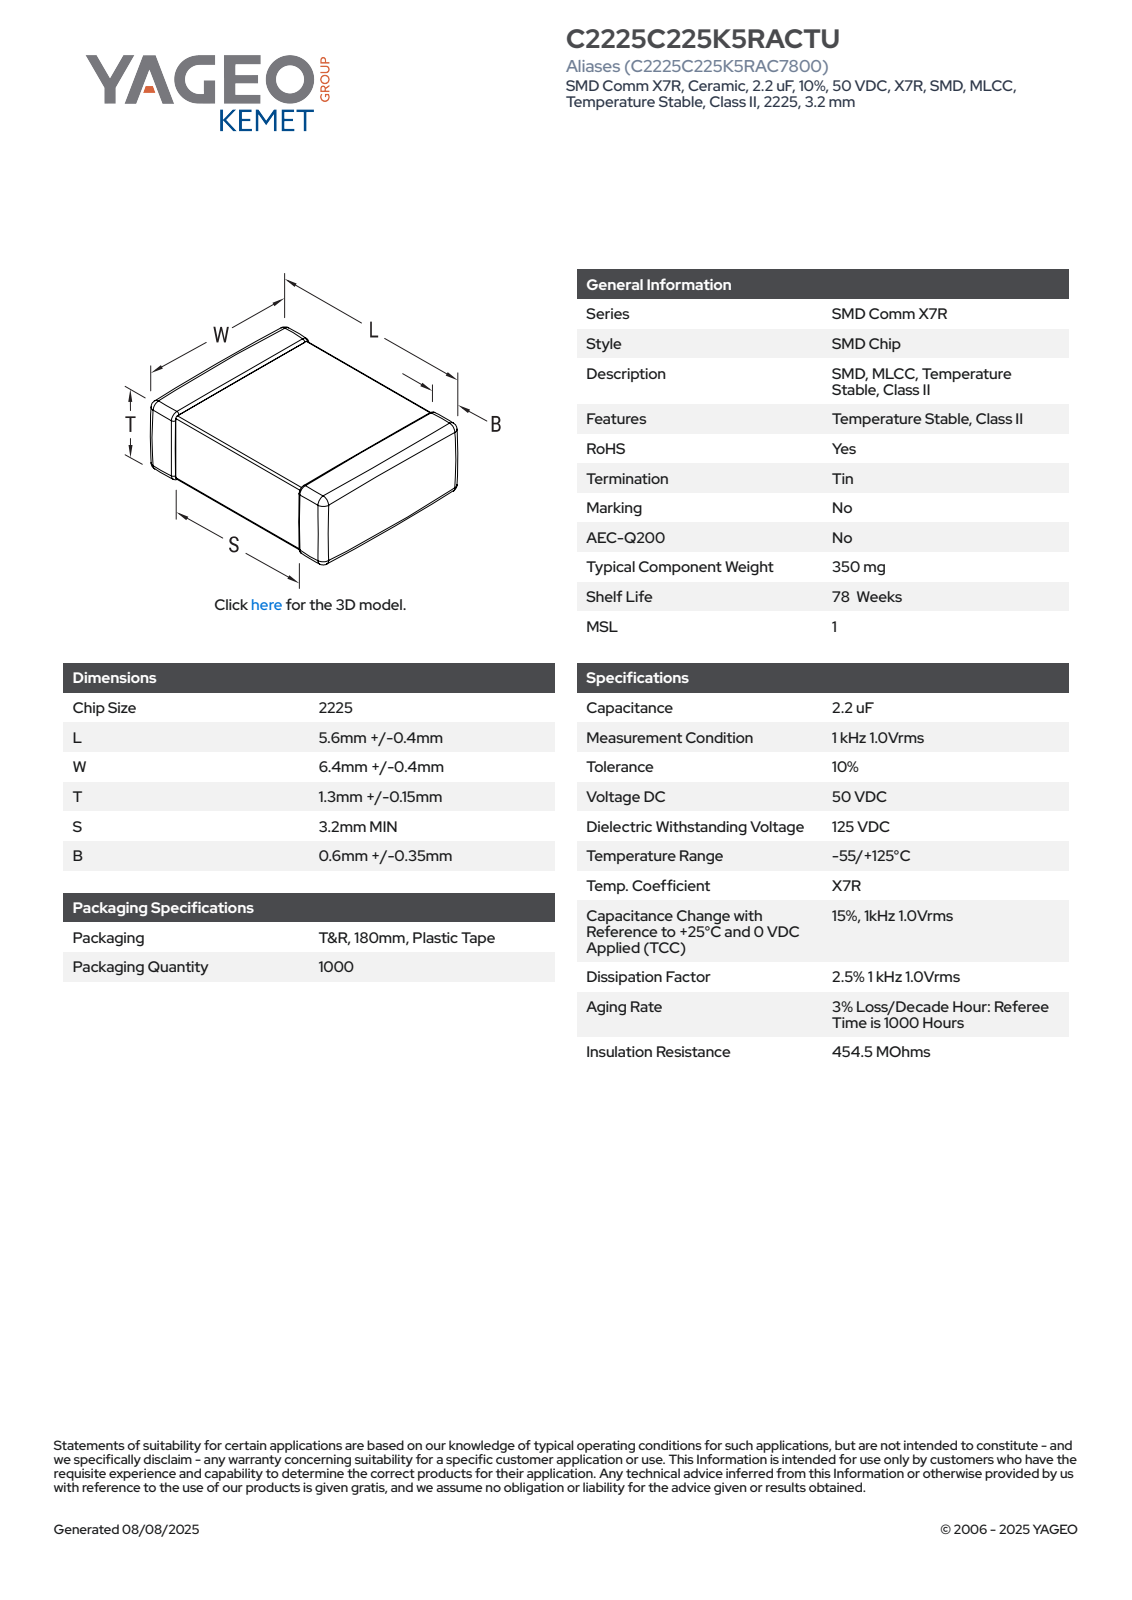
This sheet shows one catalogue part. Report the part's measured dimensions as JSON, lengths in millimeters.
{"part_name": "CCS_CCSTDNOS_2225_L6W6.8T1.45B0.95", "step_written_by": "SolidWorks 2014 (AUTOMOTIVE_DESIGN)", "units": "millimeters", "bodies": {"solids": 4, "faces": 125, "planar": 71, "cylindrical": 38, "other": 16}, "overall_size": [6.8, 6, 1.45], "volume_mm3": 50, "surface_area_mm2": 114, "partial_cylinders_radius": [[0.14, 24]], "face_to_face_distances": [1.17, 1.31, 1.45, 6, 6.52, 6.66, 6.8, 3.33, 0.43, 3.47]}
